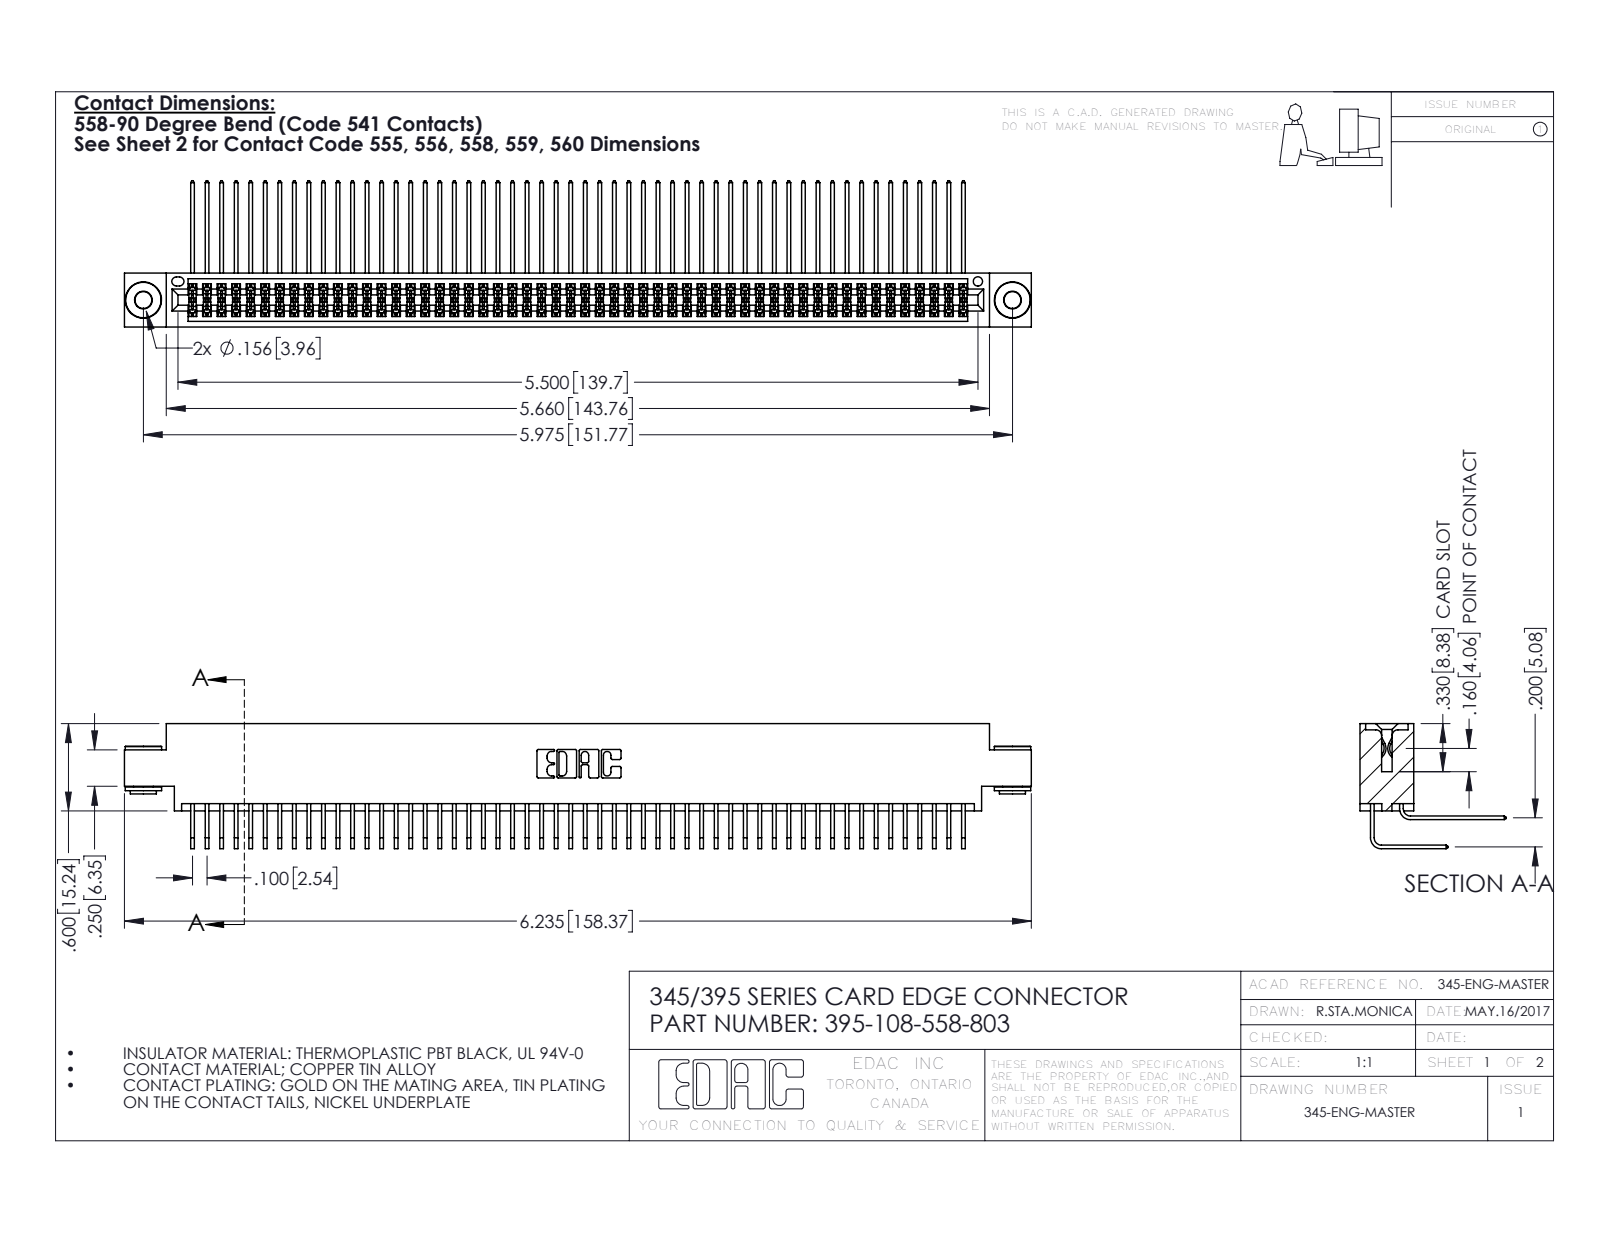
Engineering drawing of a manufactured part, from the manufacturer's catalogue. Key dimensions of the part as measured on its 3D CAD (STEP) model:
Part name (STEP PRODUCT): 345-292-001_558 559 Tail - 1; 345 Part_0.170 Offset - 0.156 Dia-TH; 345-292-001_558 Tail - 2; 345-250-002_345-250-002-102 (+1 more)
STEP written by: SolidWorks 2016 (CONFIG_CONTROL_DESIGN)
Units: inches
Bodies: 111 solids, 5784 faces (3874 planar, 1902 cylindrical, 8 other)
Overall size (bounding box): 6.235 × 1.005 × 0.859
Volume: 0.978 in³ · Surface area: 42.16 in²
Round holes (diameter × count): ⌀0.116 ×2, ⌀0.156 ×2, ⌀0.064 ×1
Round bosses / shafts (diameter × count): ⌀0.25 ×2, ⌀0.18 ×2, ⌀0.136 ×2
Partial cylindrical surfaces — rounded edges, fillets, slot ends (radius × count): R0.006 ×162, R0.01 ×22, R0.007 ×6, R0.031 ×6, R0.026 ×3, R0.014 ×2, R0.019 ×2, R0.022 ×2
Main face-to-face distances: 0.072, 0.298, 0.2, 0.37, 0.098, 0.272, 0.025, 0.225, 0.175, 0.025
Hole centre spacings: 0.27, 5.739, 5.975
